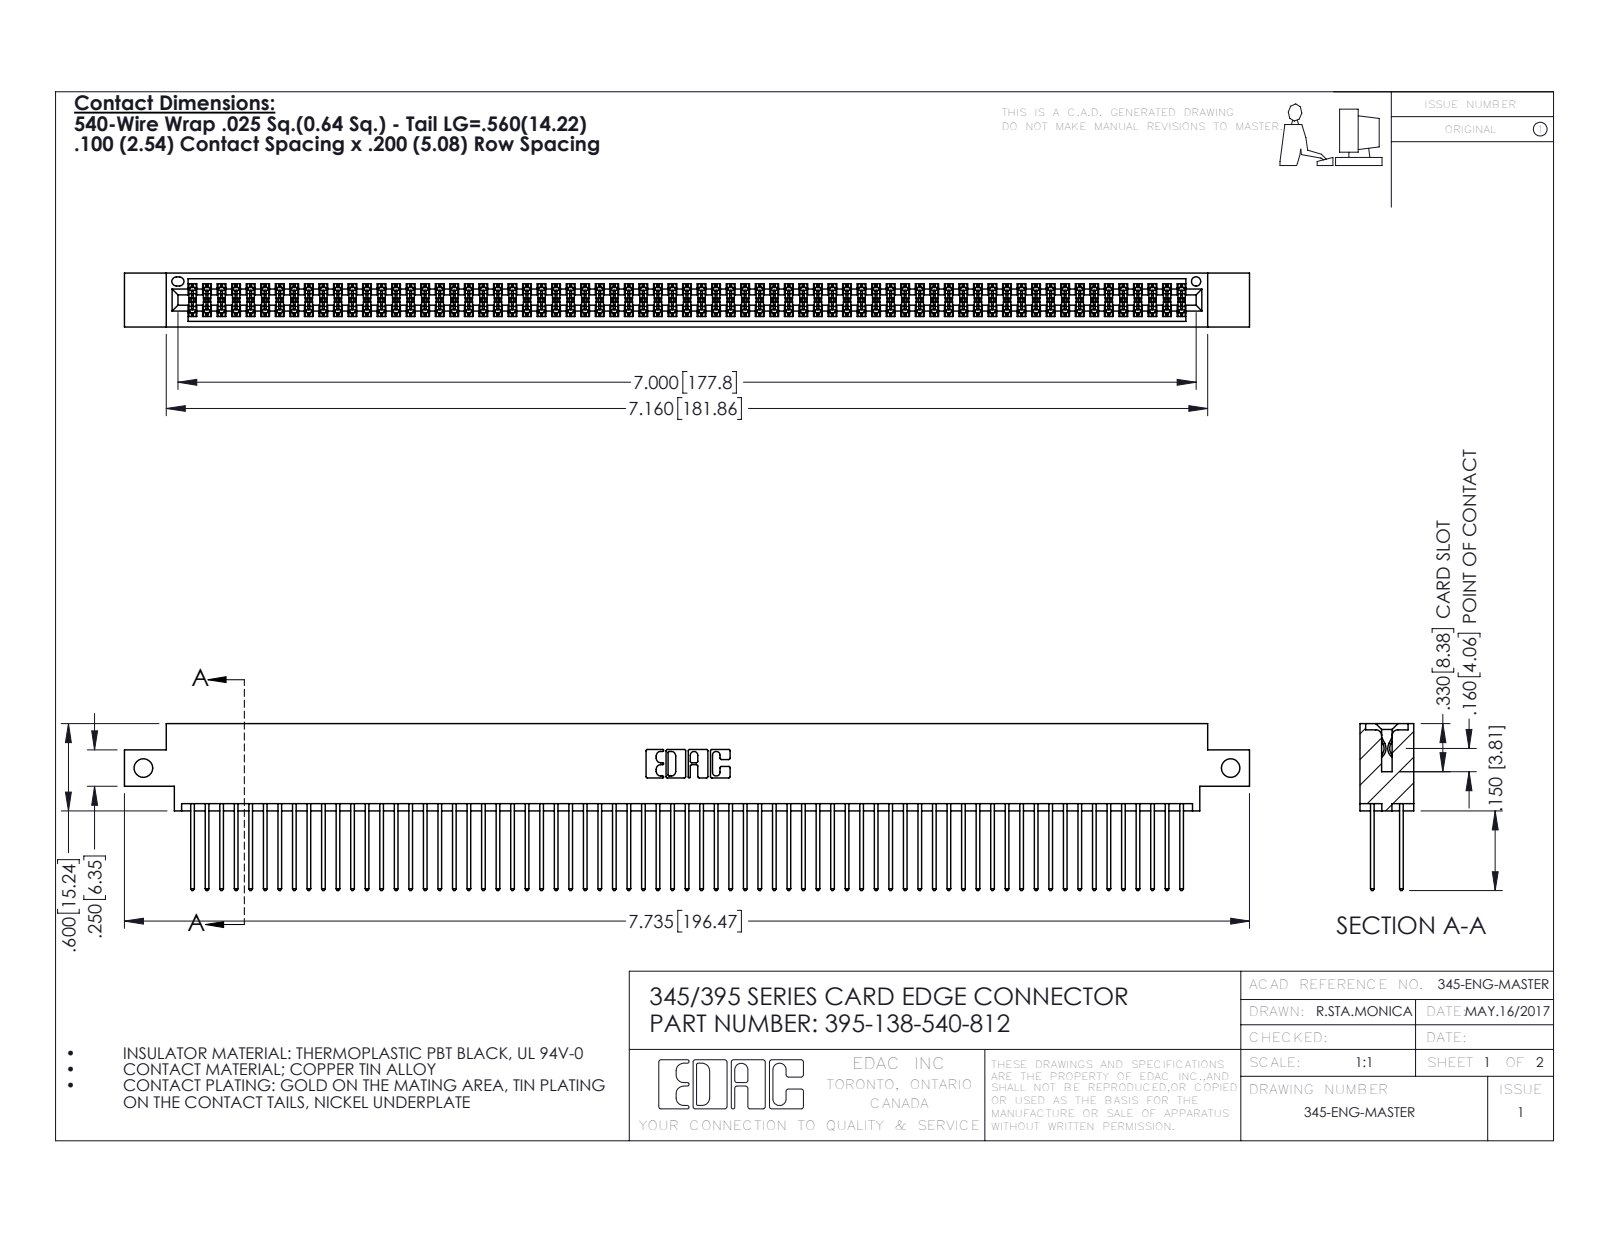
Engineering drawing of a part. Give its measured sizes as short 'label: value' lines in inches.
name: 345-292-001_345-293-140; 345 Part_0.170 Offset - Side Mount; 395-138-540-812
written by: SolidWorks 2016 (CONFIG_CONTROL_DESIGN)
unit: in
bodies: 139 solids, 7030 faces (4638 planar, 2392 cylindrical, 0 other)
size: 7.735 × 1.147 × 0.37
volume: 1.2 in³; area: 49.63 in²
holes: 2× ⌀0.128, 1× ⌀0.064
rounds: 207× R0.006, 138× R0.01, 22× R0.01, 6× R0.007, 6× R0.031, 3× R0.026, 2× R0.014, 2× R0.019
face distances: 0.072, 0.298, 0.2, 0.098, 0.272, 0.025, 0.37, 0.225, 0.175, 0.149
hole spacings: 7.475
